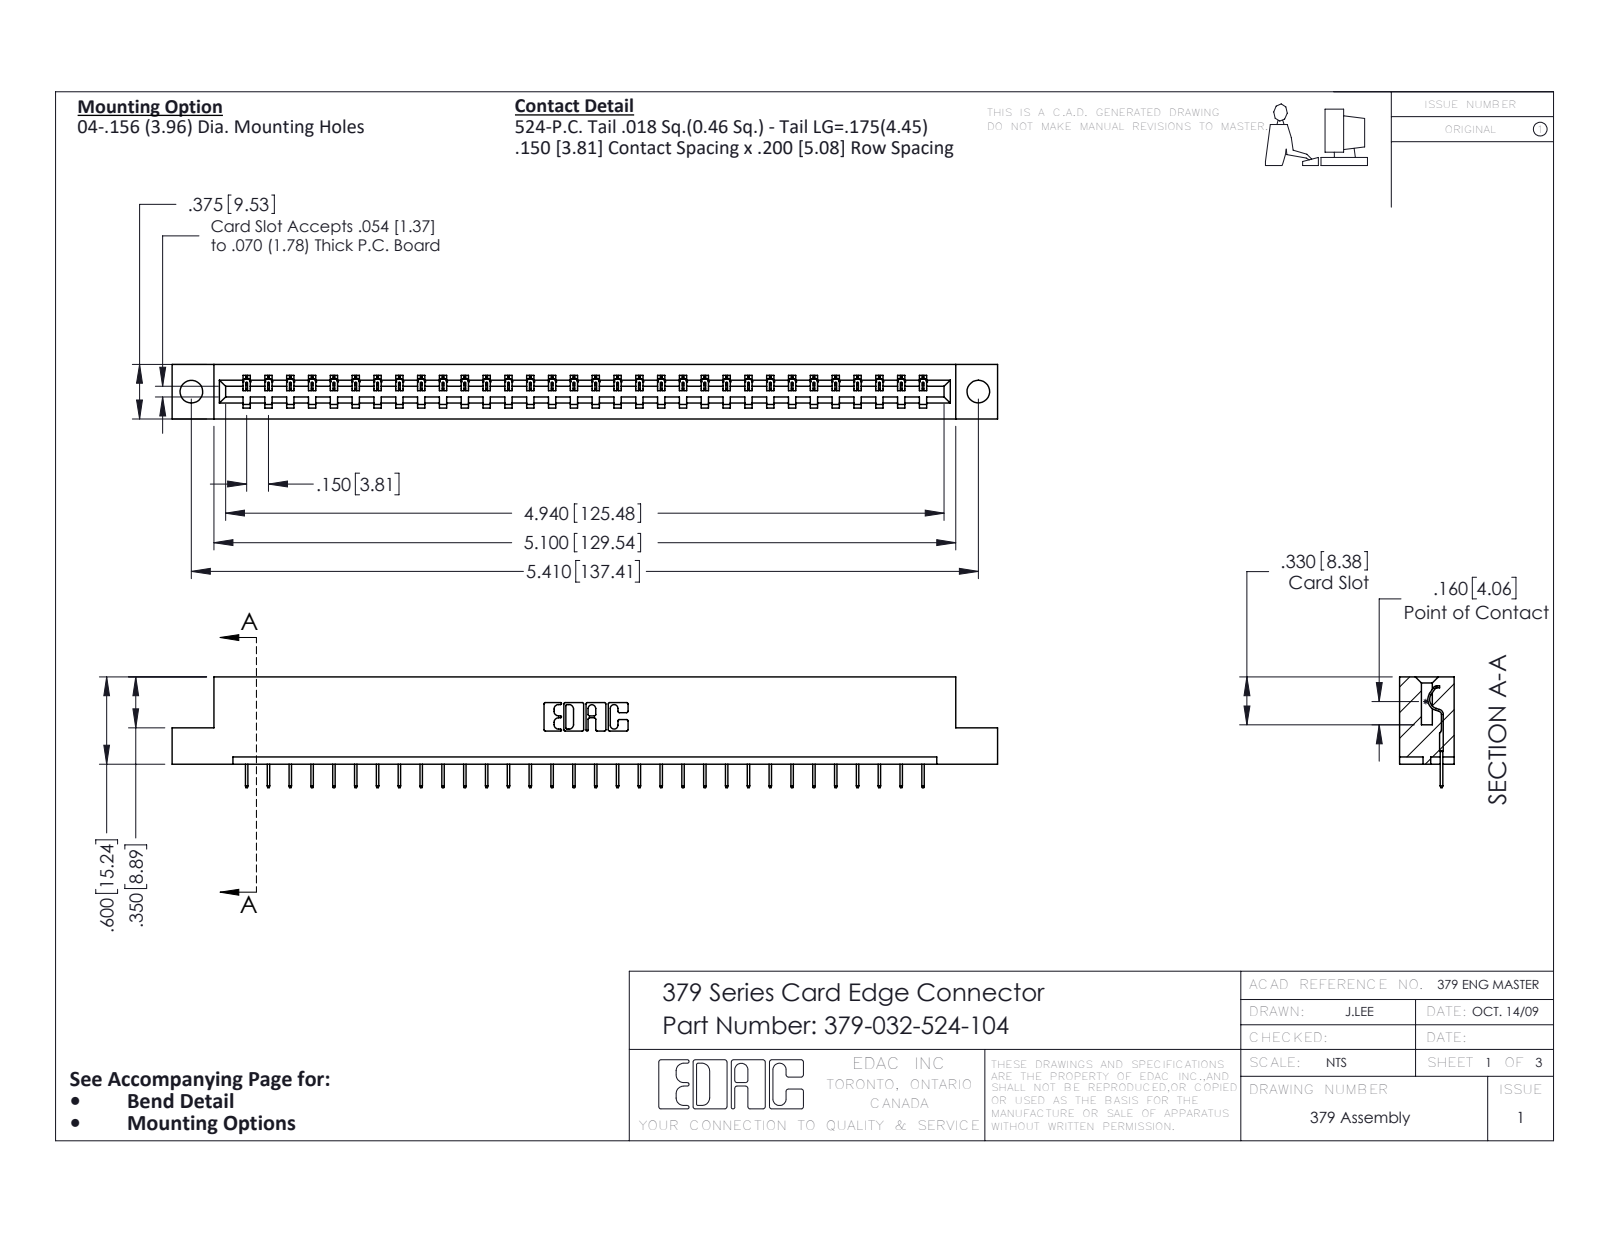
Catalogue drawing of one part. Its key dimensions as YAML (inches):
part_name: "379 Part_Flush - .156 Dia - TH; 379-032-524-104; 345-292-001_345-293-124"
step_written_by: "SolidWorks 2016 (CONFIG_CONTROL_DESIGN)"
units: inches
bodies: {solids: 33, faces: 2098, planar: 1606, cylindrical: 492, other: 0}
overall_size: [5.675, 0.762, 0.375]
volume: 0.904
surface_area: 22.4
round_holes:
  - {diameter: 0.156, count: 2}
partial_cylinders:
  - {radius: 0.006, count: 64}
  - {radius: 0.01, count: 22}
  - {radius: 0.007, count: 6}
  - {radius: 0.031, count: 6}
  - {radius: 0.026, count: 3}
  - {radius: 0.014, count: 1}
  - {radius: 0.022, count: 1}
  - {radius: 0.024, count: 1}
face_to_face_distances: [0.3, 0.075, 0.375, 0.225, 0.6, 0.55, 0.2, 0.15, 0.15, 0.15]
hole_center_spacings: [5.41]
